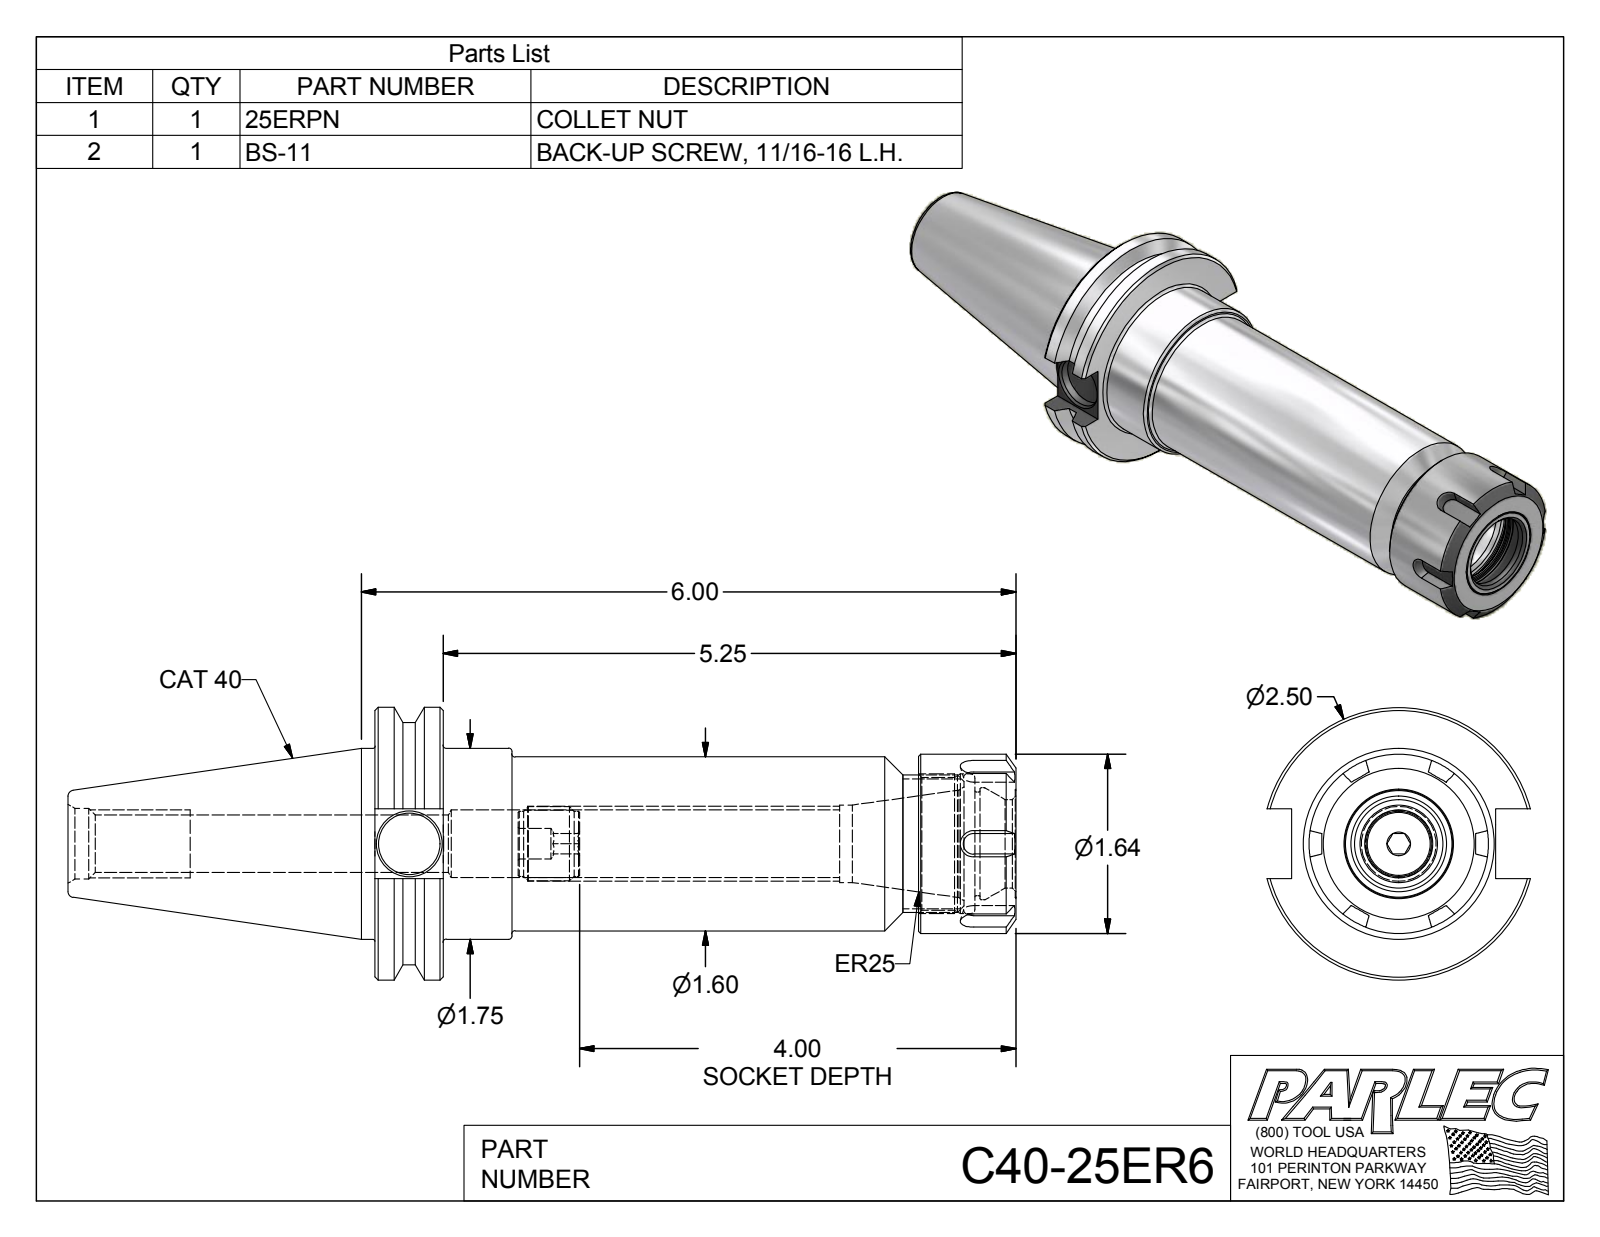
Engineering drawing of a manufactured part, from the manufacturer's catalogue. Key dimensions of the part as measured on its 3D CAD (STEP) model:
Part name (STEP PRODUCT): C40-25ER6; C40-25ER6-1; 25ERPN; BS-11
STEP written by: Autodesk Inventor 2012 (AUTOMOTIVE_DESIGN)
Units: inches
Bodies: 3 solids, 117 faces (43 planar, 25 cylindrical, 49 other)
Overall size (bounding box): 8.688 × 2.5 × 2.417
Volume: 14.81 in³ · Surface area: 76.46 in²
Round holes (diameter × count): ⌀0.28 ×1, ⌀0.527 ×1, ⌀0.563 ×1, ⌀0.62 ×1, ⌀0.648 ×1, ⌀0.71 ×1, ⌀0.811 ×1, ⌀0.95 ×1, ⌀1.027 ×1, ⌀1.217 ×1, ⌀1.28 ×1
Round bosses / shafts (diameter × count): ⌀2.5 ×1, ⌀2.219 ×1, ⌀1.75 ×1, ⌀1.643 ×1, ⌀1.595 ×1, ⌀1.26 ×1, ⌀0.681 ×1, ⌀0.595 ×1
Main face-to-face distances: 0.625, 5.875, 5.25, 4.982, 4.357, 0.893, 5.5, 4.875, 0.518, 0.375
